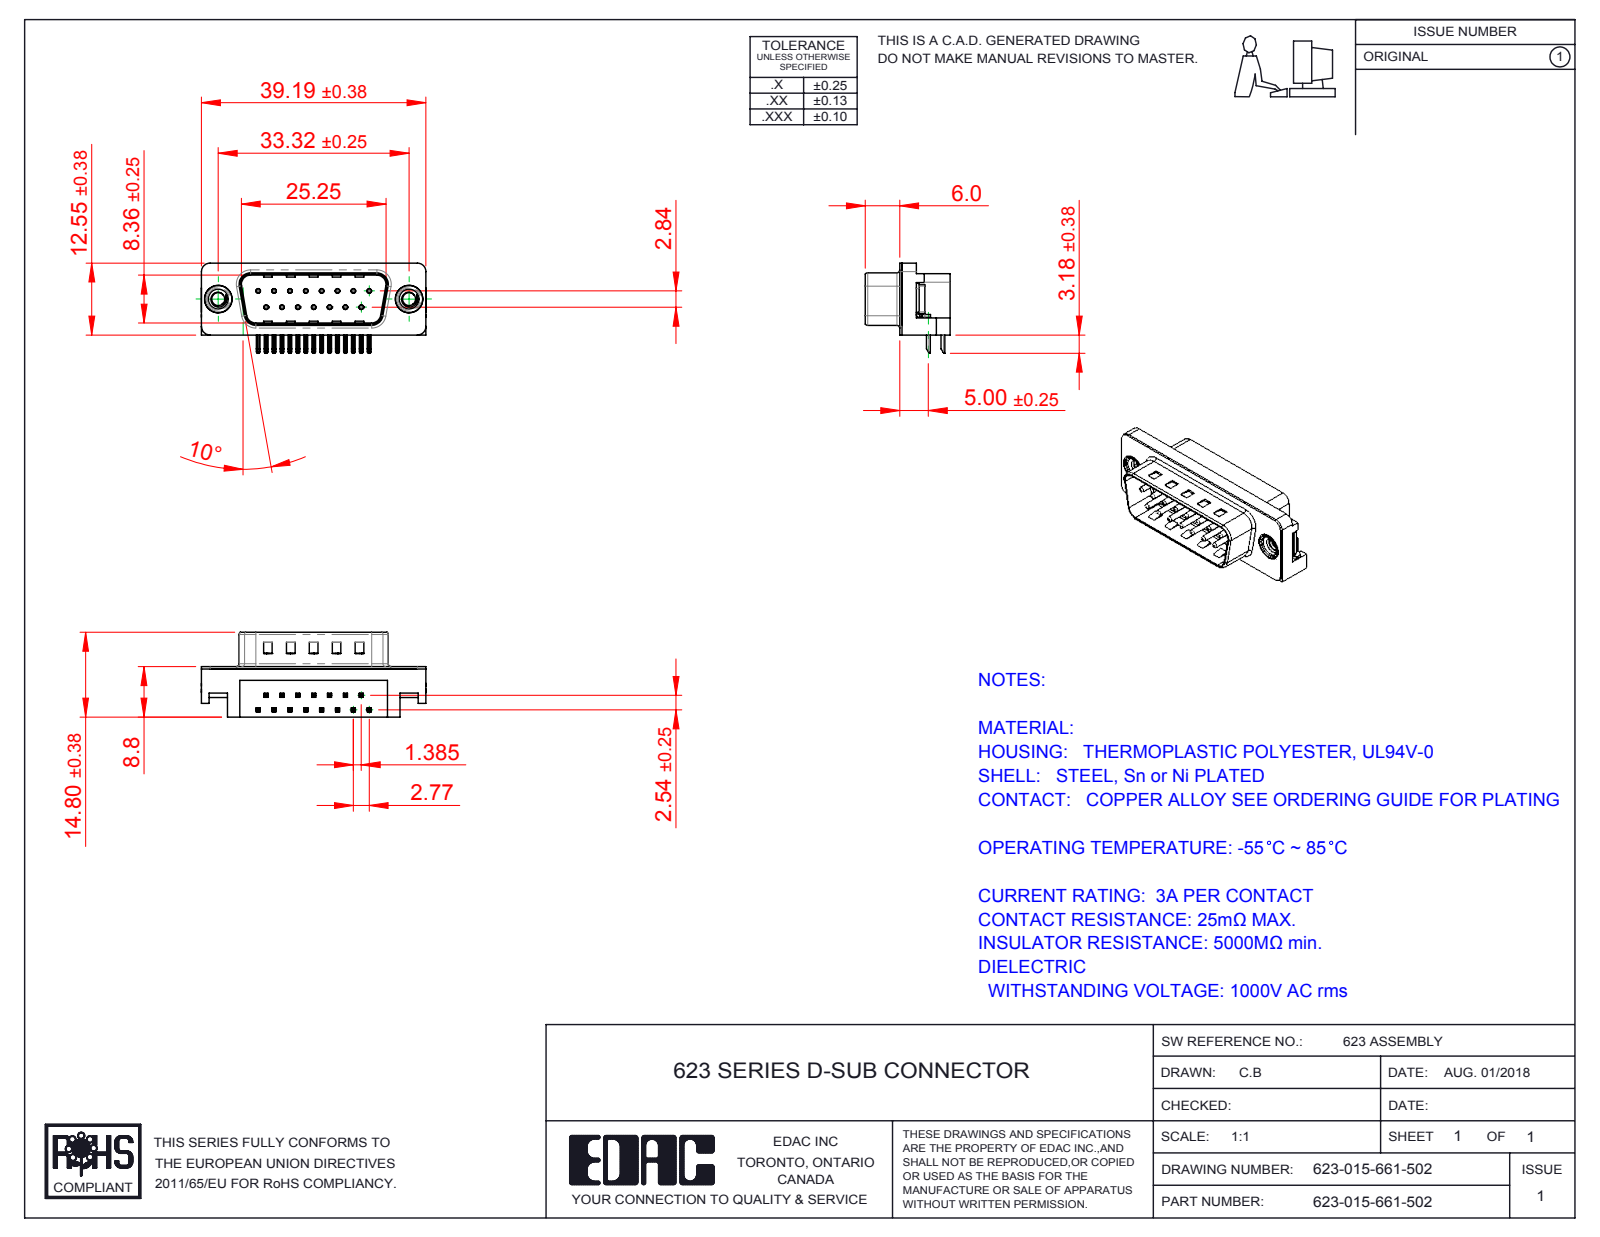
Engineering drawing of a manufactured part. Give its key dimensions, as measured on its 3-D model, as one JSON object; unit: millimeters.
{"part_name": "623-015-661-502; 623 Housing_15 Socket; 623 Contact Bottom; 623 Non Board Mount (+3 more)", "step_written_by": "SolidWorks 2016 (CONFIG_CONTROL_DESIGN)", "units": "millimeters", "bodies": {"solids": 21, "faces": 1467, "planar": 893, "cylindrical": 435, "other": 139}, "overall_size": [39.22, 15.73, 14.8], "volume_mm3": 3319, "surface_area_mm2": 4885, "round_holes": [[0.35, 15], [0.8, 15], [2.26, 2], [4, 2], [4.8, 2], [5, 2]], "round_bosses_or_shafts": [[0.75, 15], [4.9, 2], [4.75, 2], [3.9, 2]], "partial_cylinders_radius": [[0.25, 68], [0.12, 30], [1, 16], [0.5, 9], [1.5, 6], [0.9, 4], [1.6, 4], [2, 4]], "face_to_face_distances": [0.4, 8.4, 2.1, 1.7, 10.46, 8.8, 10.86, 8.76, 5.9, 2.9], "hole_center_spacings": [3.16, 2.77, 5.54, 8.31, 11.08, 5.03, 5.04, 7.48]}
